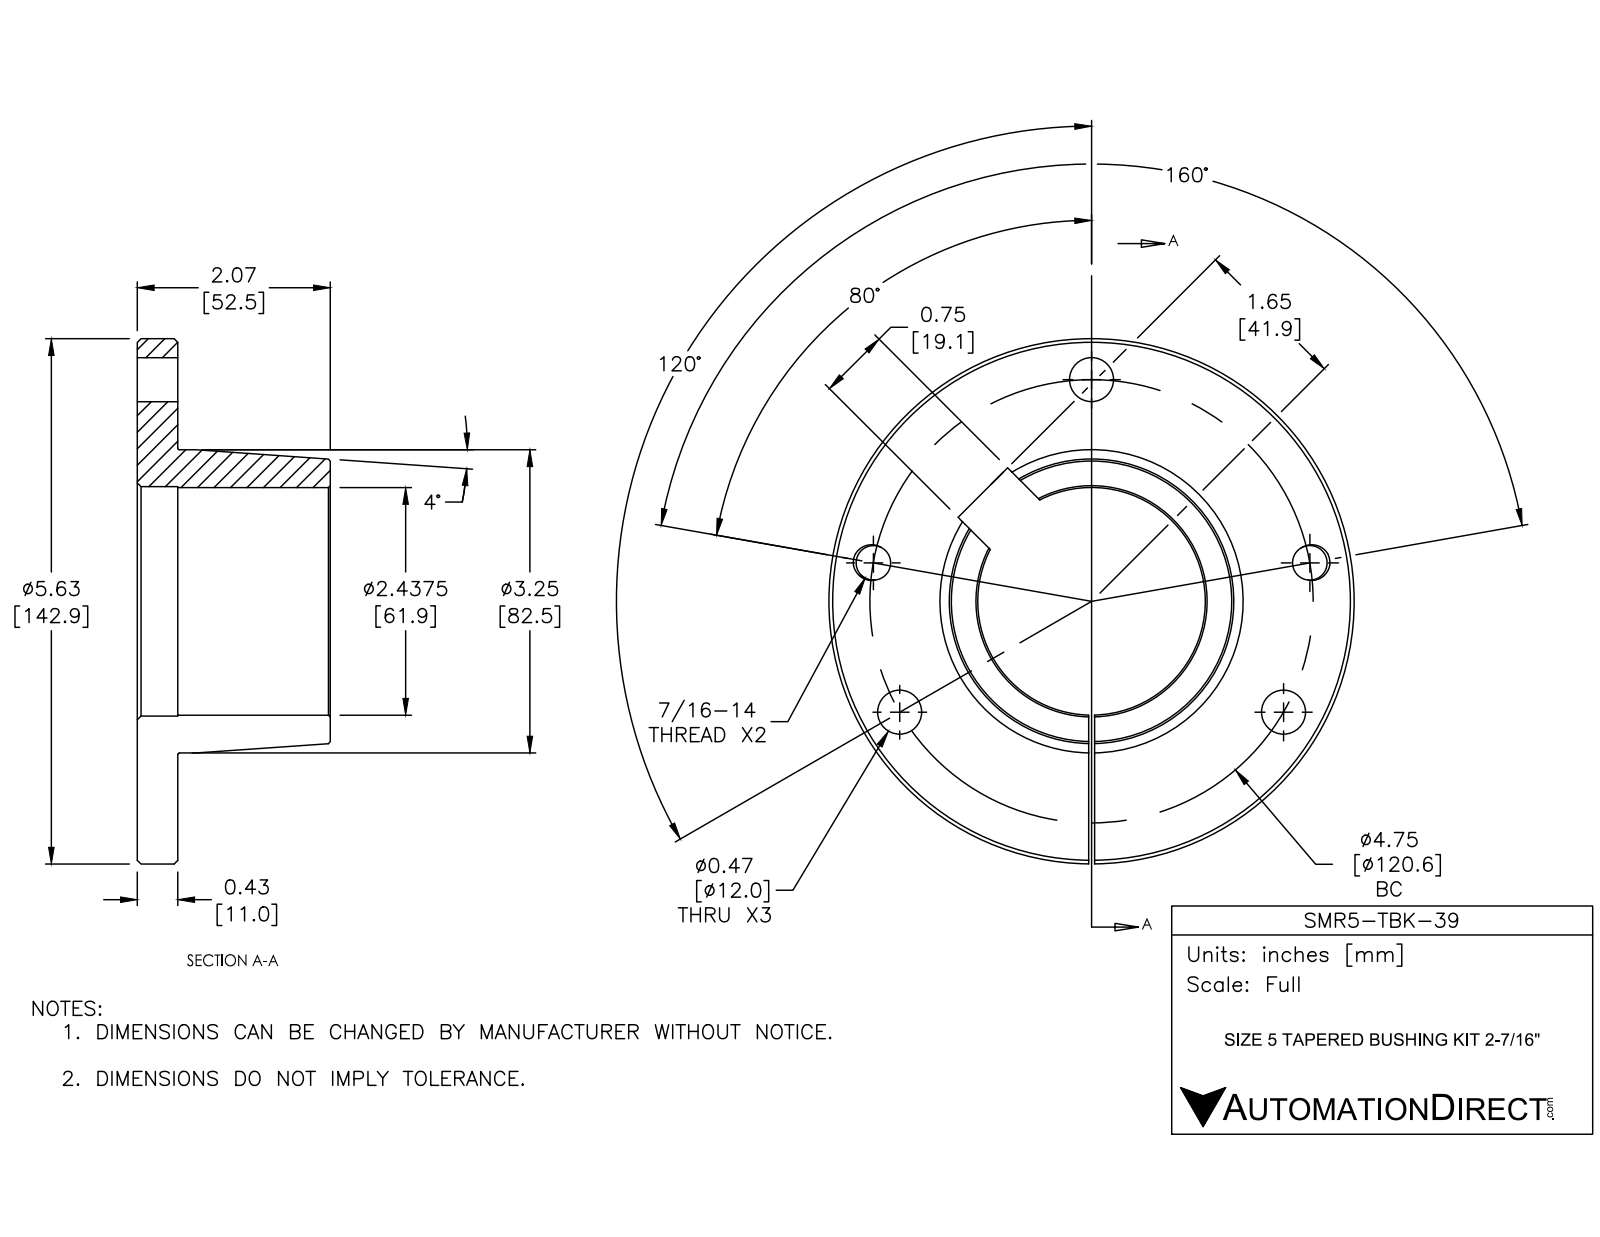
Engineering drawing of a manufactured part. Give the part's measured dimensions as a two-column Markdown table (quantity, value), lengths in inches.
| quantity | value |
| --- | --- |
| part name | SMR5-TBK-39 |
| STEP written by | SolidWorks 2016 (AUTOMOTIVE_DESIGN) |
| units | inches |
| bodies | 1 solid, 98 faces (11 planar, 67 cylindrical, 20 other) |
| overall size | 5.626 × 5.626 × 2.067 |
| volume | 12.86 in³ |
| surface area | 80.55 in² |
| round holes (diameter × count) | 0.472 × 3, 0.37 × 2, 0.43 × 2, 2.438 × 1, 2.457 × 1 |
| round bosses / shafts (diameter × count) | 5.626 × 1, 3.247 × 1 |
| main face-to-face distances | 0.433, 2.067, 1.634, 0.063, 0.75 |
| hole center spacings | 2.374, 4.112, 4.676, 1.624, 3.052 |
